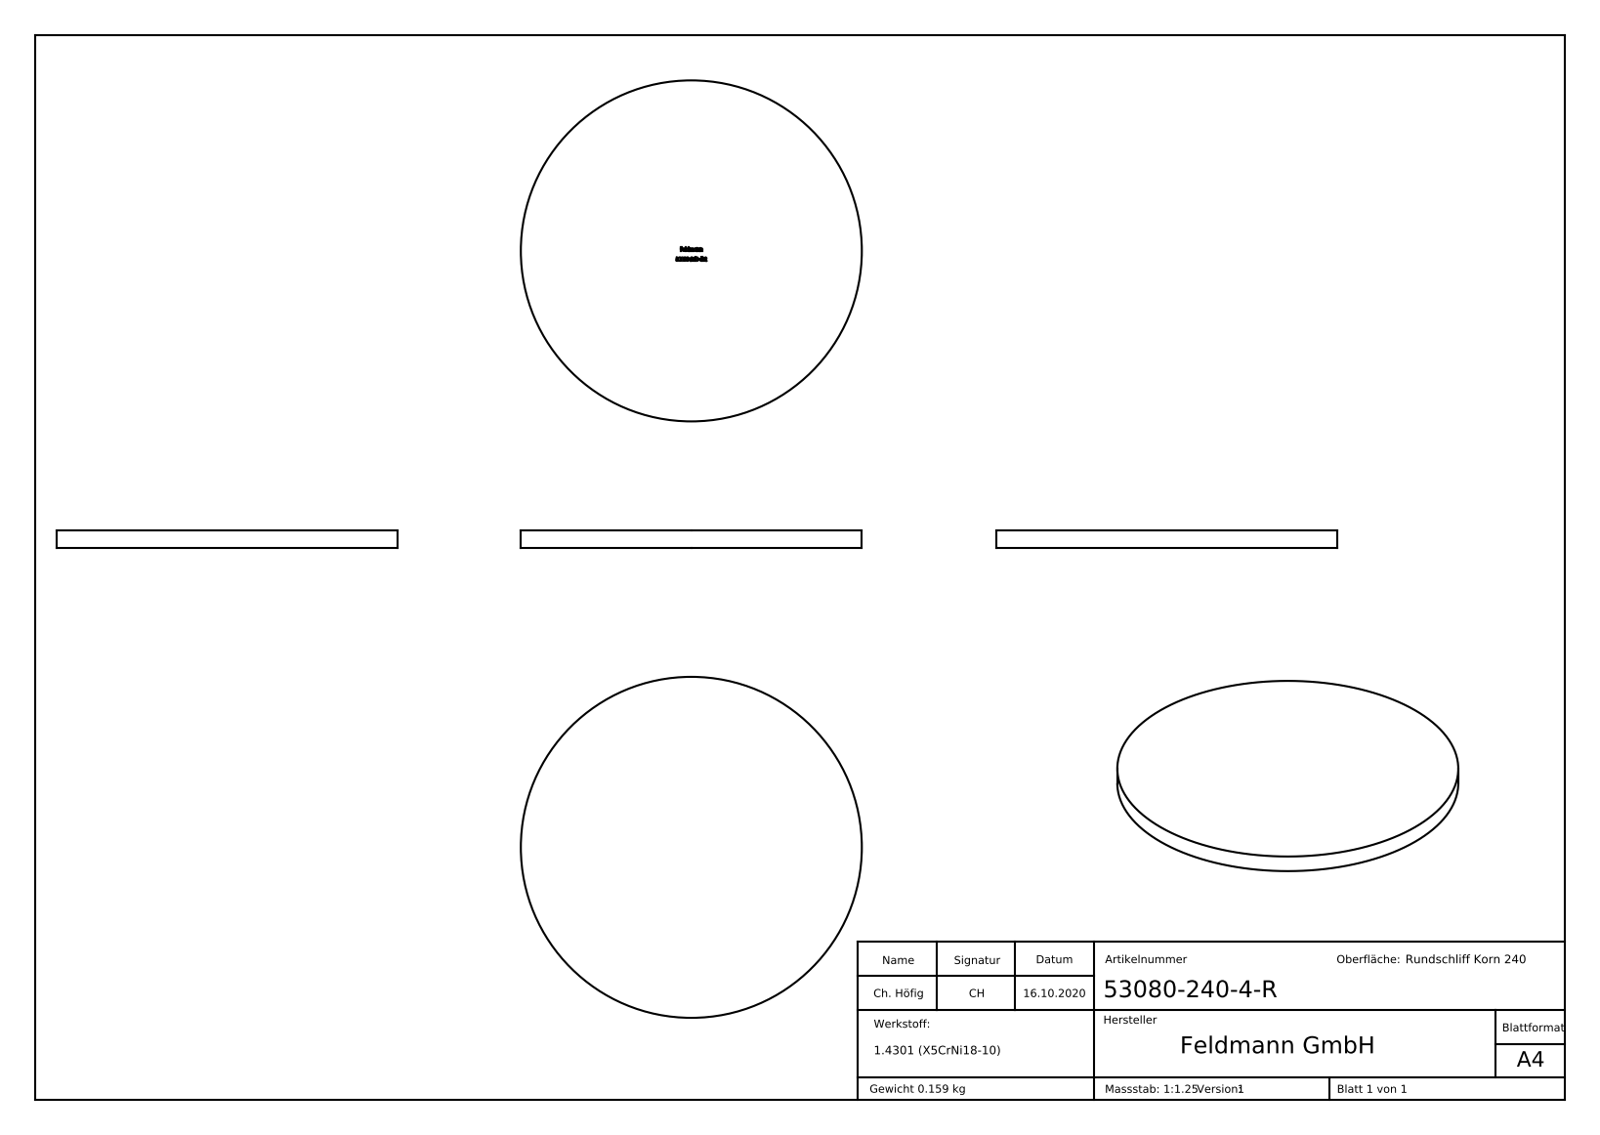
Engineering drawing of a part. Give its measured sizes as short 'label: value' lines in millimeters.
name: 53080-240-4-R
written by: SolidWorks 2018 (CONFIG_CONTROL_DESIGN)
unit: mm
bodies: 1 solid, 279 faces (152 planar, 2 cylindrical, 125 other)
size: 80 × 80 × 4
volume: 20 106 mm³; area: 11 065 mm²
bosses: 1× ⌀80
face distances: 4, 3.9, 0.67, 1.21, 3.75, 1.78, 0.98, 0.83, 2.77, 0.53
